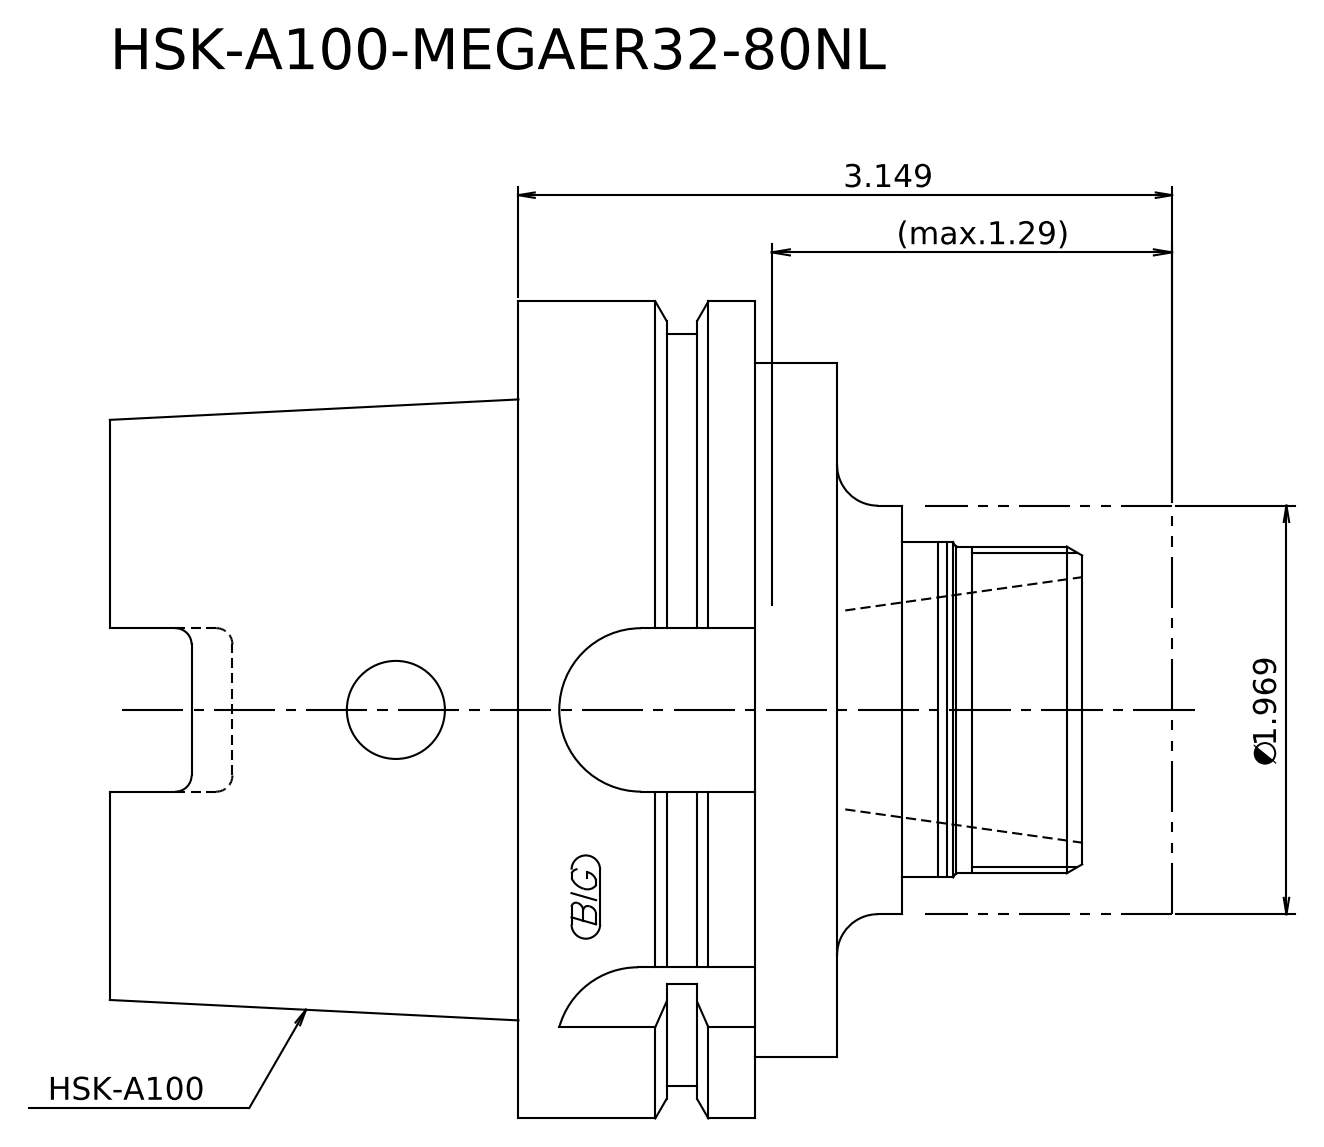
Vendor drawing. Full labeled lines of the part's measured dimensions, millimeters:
STEP written by: Kubotek KeyCreator 2011 V10.0.2 (22737) (automotive_design)
Units: millimetres
Bodies: 2 solids, 24 faces (10 planar, 8 cylindrical, 6 other)
Overall size (bounding box): 130 × 100 × 100
Volume: 596 234 mm³ · Surface area: 52 295 mm²
Round bosses / shafts (diameter × count): ⌀100 ×1, ⌀92 ×1, ⌀85 ×1, ⌀50 ×1, ⌀41 ×1, ⌀40 ×1
Main face-to-face distances: 50, 39, 89, 10, 29, 79, 10.8, 20.8, 49.8, 99.8
